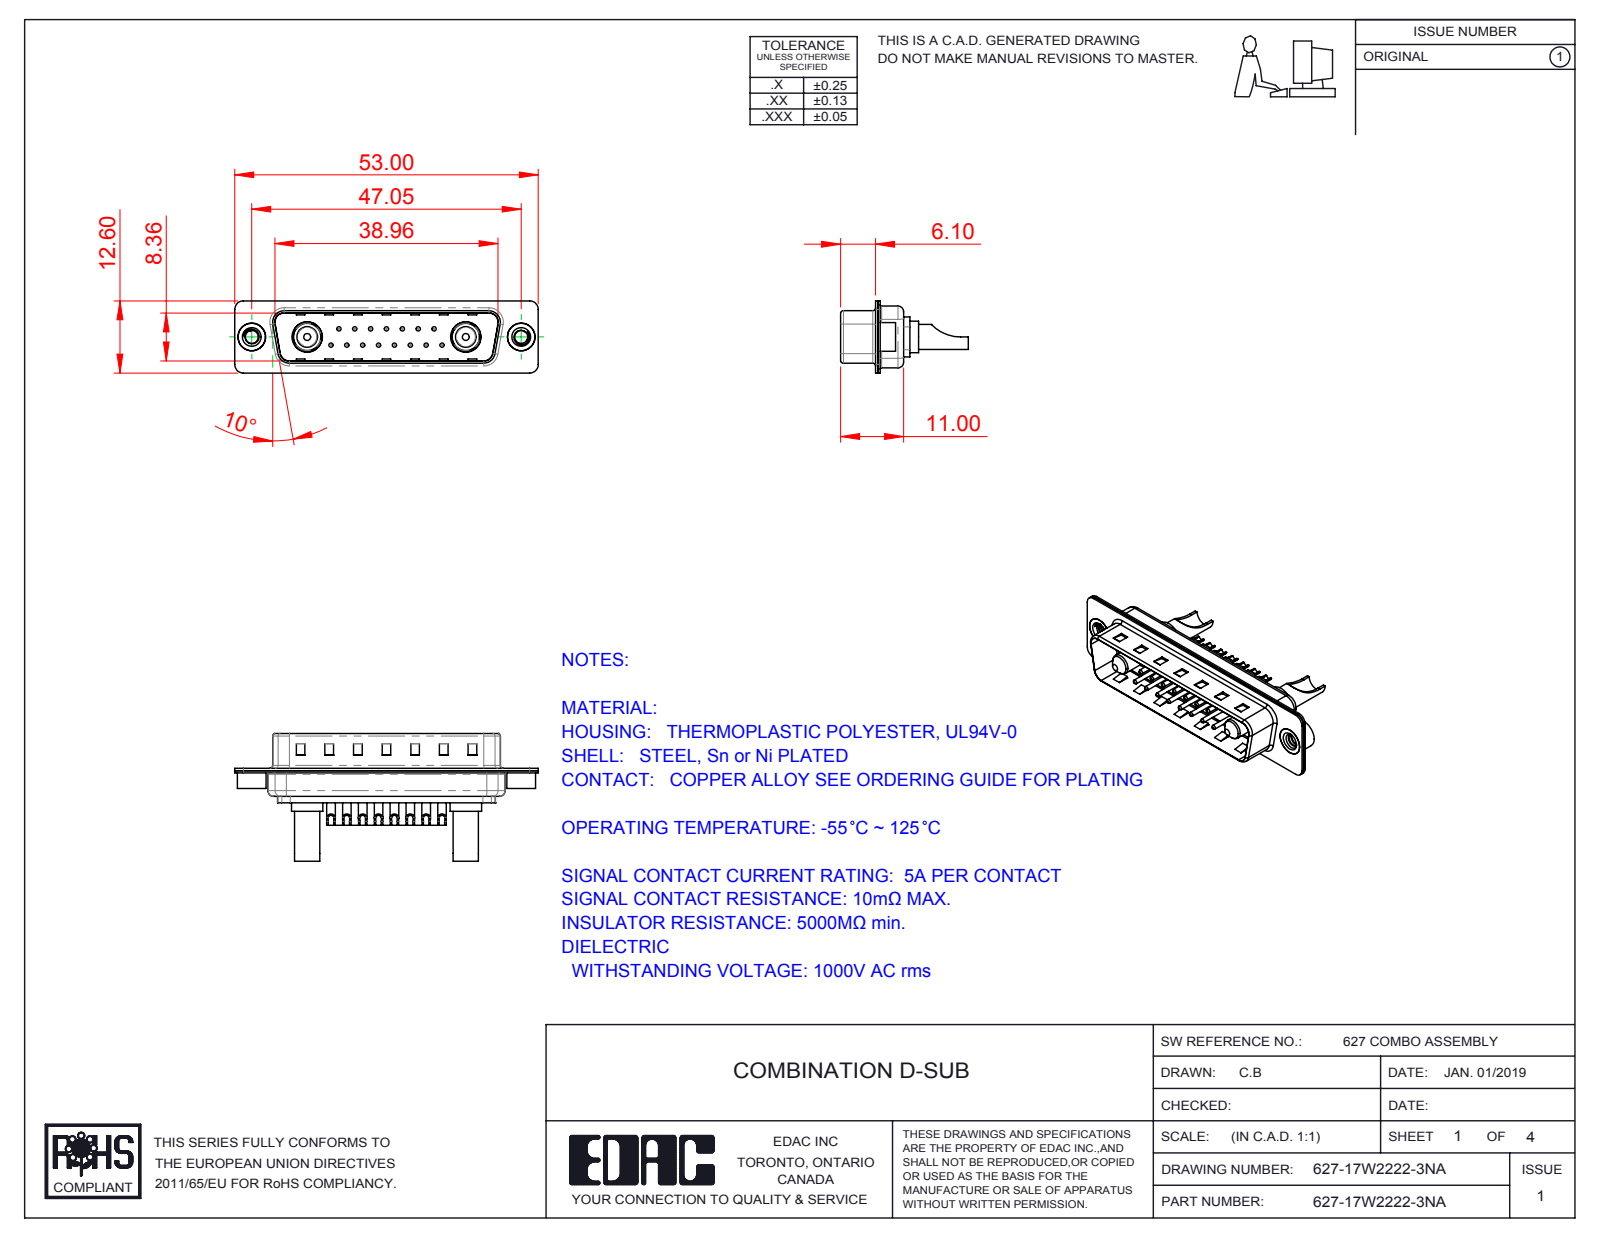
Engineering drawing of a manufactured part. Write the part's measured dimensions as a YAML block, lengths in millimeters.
part_name: "627Combo Shell Front_25 Contacts; 627Combo Shell Rear_25 Contacts; 627Combo Contact Row 2_22; 627Combo Threaded Rivet_2 (+5 more)"
step_written_by: "SolidWorks 2016 (CONFIG_CONTROL_DESIGN)"
units: millimeters
bodies: {solids: 24, faces: 1022, planar: 332, cylindrical: 422, other: 268}
overall_size: [53, 22.3, 12.6]
volume: 2928
surface_area: 7122
round_holes:
  - {diameter: 0.75, count: 15}
  - {diameter: 1, count: 15}
  - {diameter: 1.6, count: 15}
  - {diameter: 2, count: 15}
  - {diameter: 2.26, count: 2}
  - {diameter: 3.5, count: 2}
  - {diameter: 4, count: 2}
  - {diameter: 4.8, count: 2}
  - {diameter: 4.85, count: 2}
  - {diameter: 5.3, count: 2}
round_bosses_or_shafts:
  - {diameter: 1.5, count: 15}
  - {diameter: 5.5, count: 2}
  - {diameter: 5.2, count: 2}
  - {diameter: 5, count: 2}
  - {diameter: 4.9, count: 2}
  - {diameter: 4.75, count: 2}
  - {diameter: 4.4, count: 2}
  - {diameter: 3.75, count: 2}
partial_cylinders:
  - {radius: 1.5, count: 16}
  - {radius: 2, count: 12}
  - {radius: 0.5, count: 8}
  - {radius: 1.6, count: 8}
  - {radius: 1, count: 6}
  - {radius: 0.25, count: 4}
  - {radius: 0.6, count: 4}
  - {radius: 0.65, count: 4}
face_to_face_distances: [0.4, 0.82, 9.58, 8.76, 1.5, 5.6, 5.2, 0.8, 1.22, 9.98]
hole_center_spacings: [3.16, 2.77, 5.54, 8.31, 5.04, 7.49, 11.08, 5.03]
